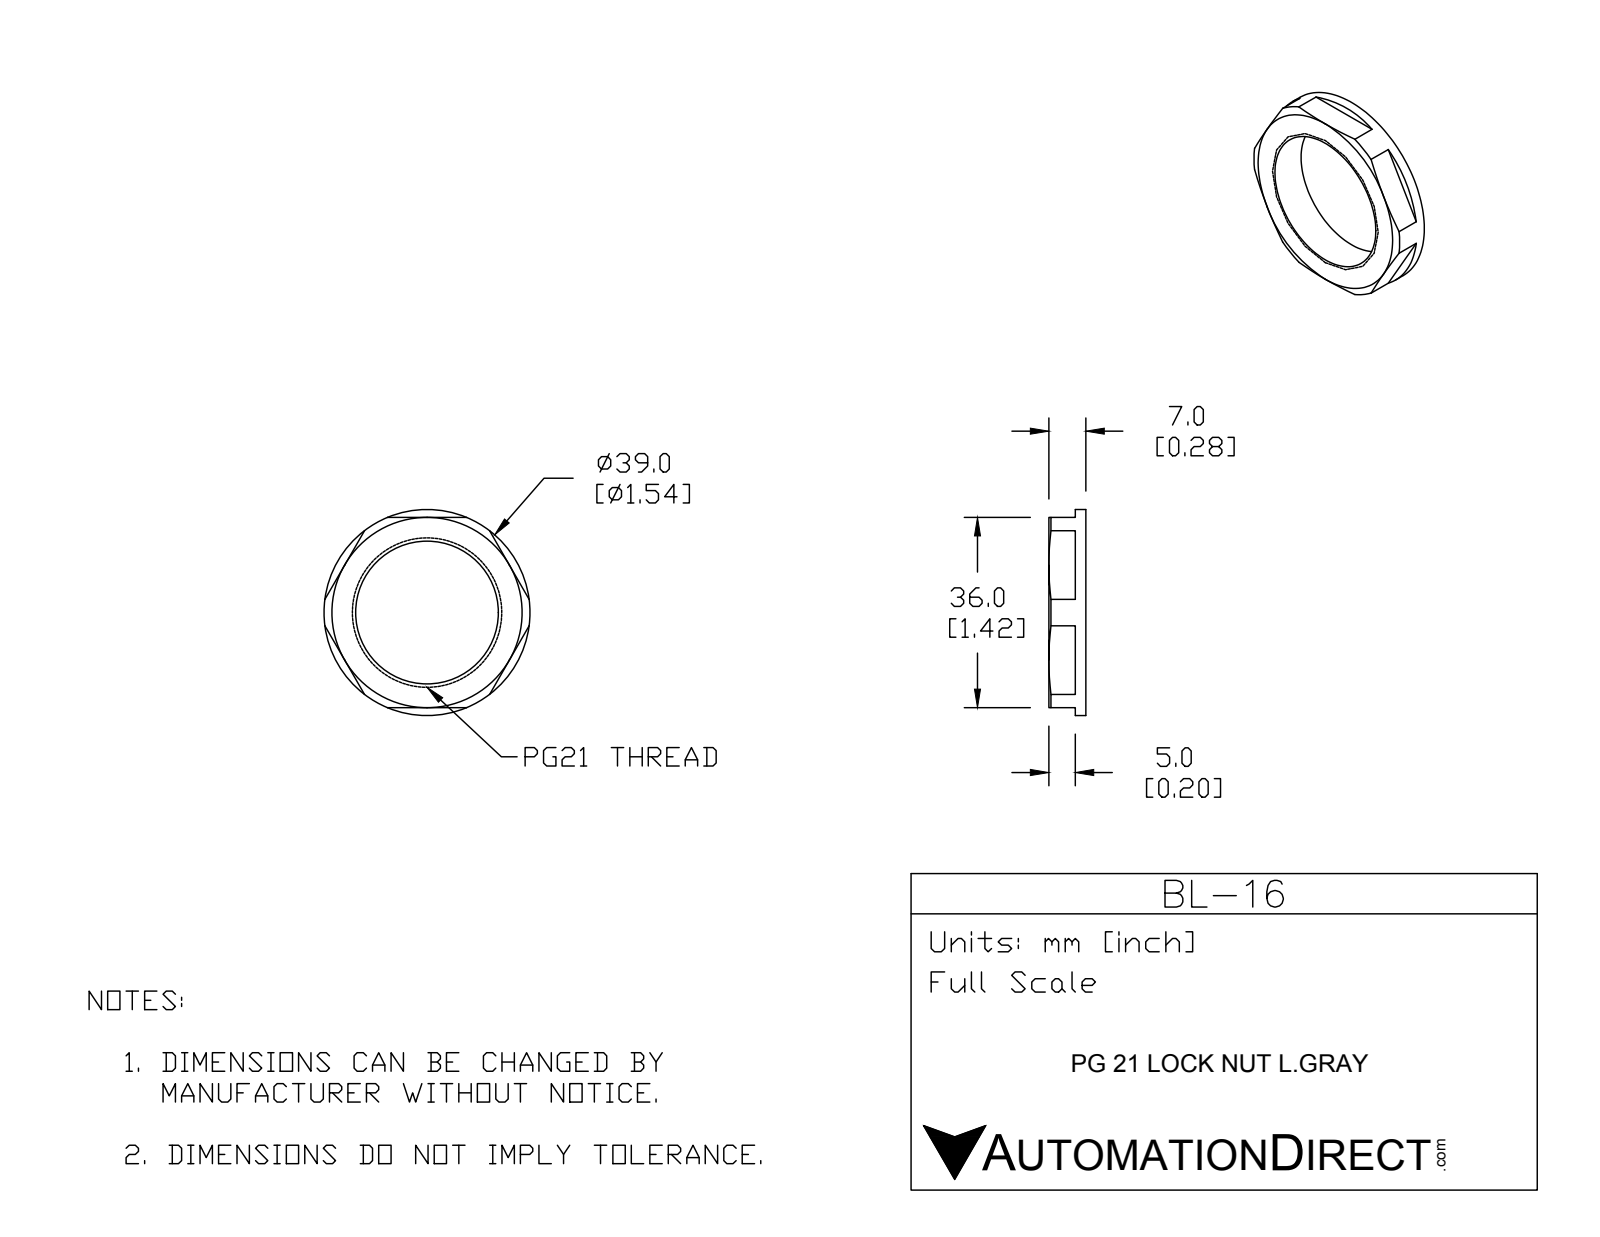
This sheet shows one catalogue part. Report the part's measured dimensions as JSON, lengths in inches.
{"part_name": "BL-16", "step_written_by": "SolidWorks 2015 (CONFIG_CONTROL_DESIGN)", "units": "inches", "bodies": {"solids": 1, "faces": 33, "planar": 17, "cylindrical": 10, "other": 6}, "overall_size": [1.535, 1.535, 0.276], "volume_in3": 0.237, "surface_area_in2": 4.132, "round_holes": [[0.059, 3], [1.063, 1]], "round_bosses_or_shafts": [[1.535, 1]], "face_to_face_distances": [0.276, 1.417, 0.079, 0.197, 0.067, 0.264], "hole_center_spacings": [0.711, 1.231, 1.231]}
